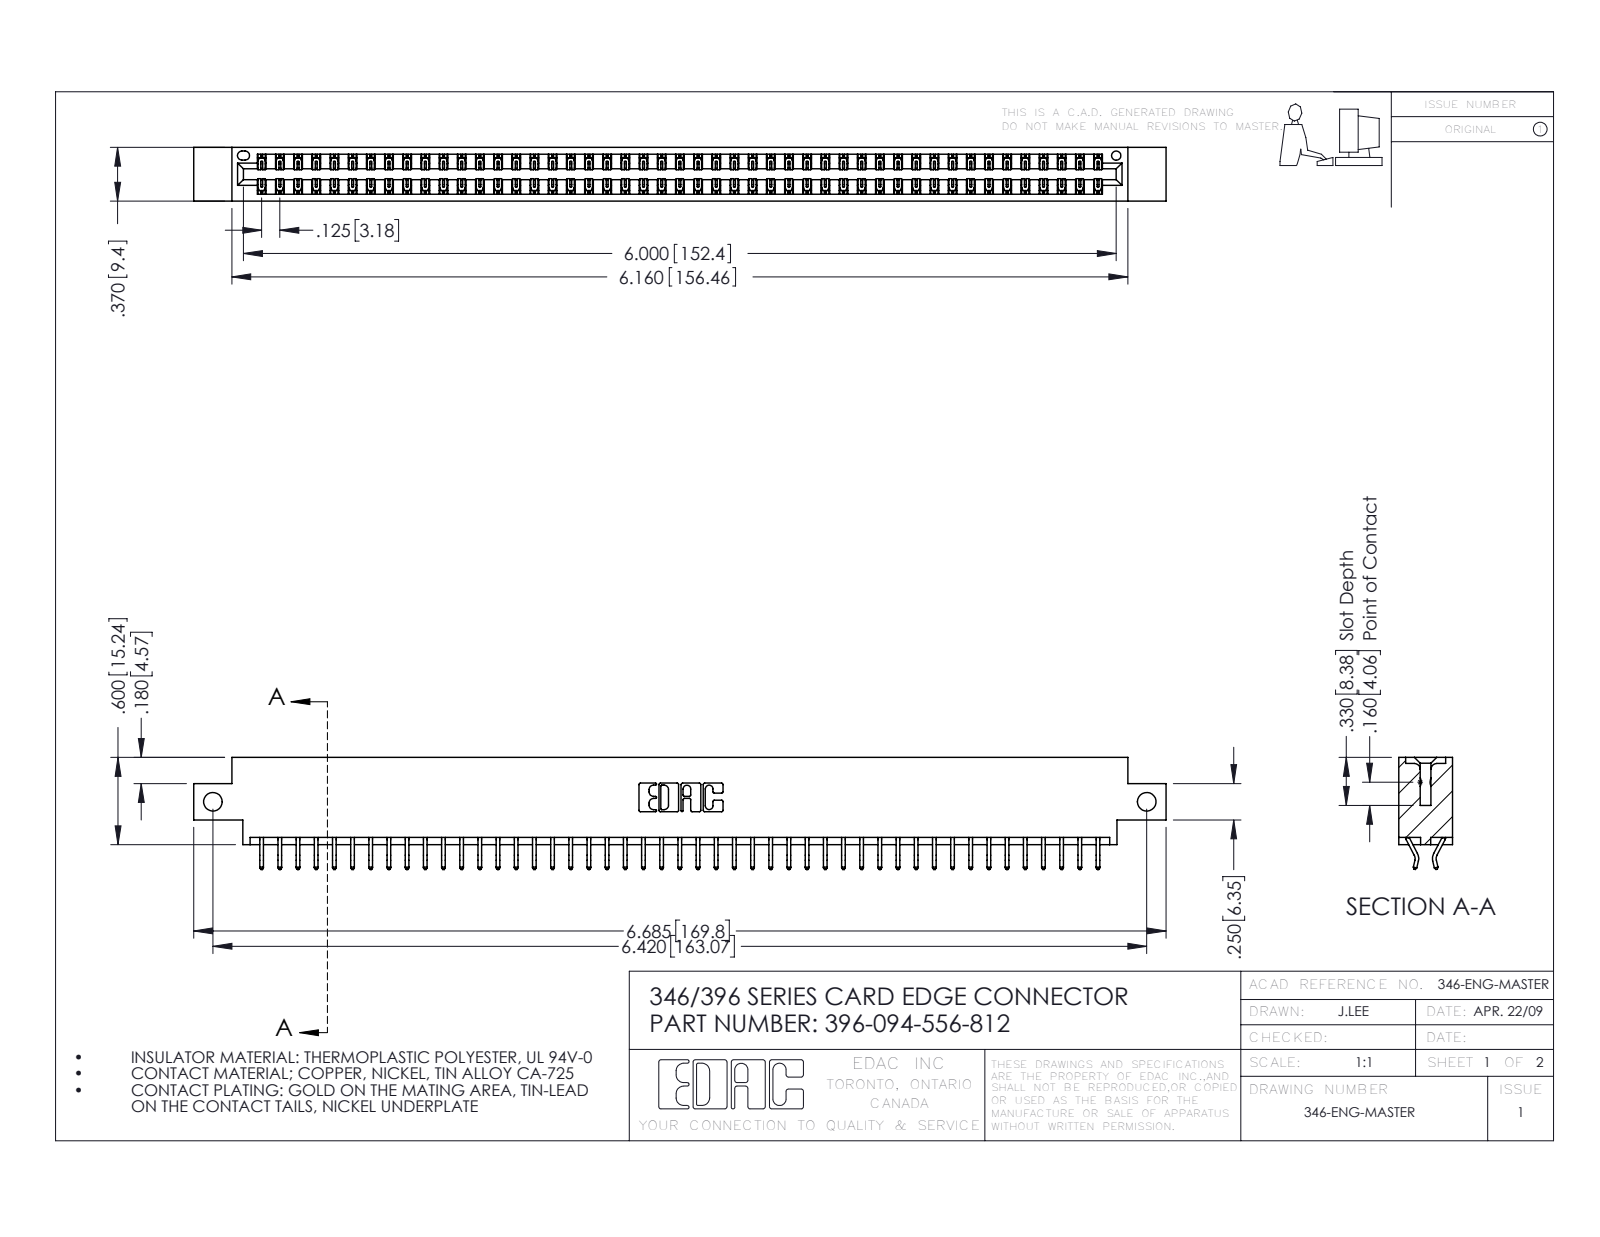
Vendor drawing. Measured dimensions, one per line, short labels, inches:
name: 346 Part_0.170 Offset - Side Mount; 396-094-556-812; 345-292-001_556 Tail
written by: SolidWorks 2016 (CONFIG_CONTROL_DESIGN)
unit: in
bodies: 95 solids, 5578 faces (3746 planar, 1832 cylindrical, 0 other)
size: 6.685 × 0.77 × 0.37
volume: 0.998 in³; area: 34.89 in²
holes: 2× ⌀0.128, 1× ⌀0.064
rounds: 141× R0.006, 22× R0.01, 6× R0.007, 6× R0.031, 3× R0.026, 2× R0.01, 2× R0.014, 2× R0.022
face distances: 0.048, 0.322, 0.37, 0.25, 0.025, 0.072, 0.298, 0.275, 0.148, 0.222
hole spacings: 6.42
